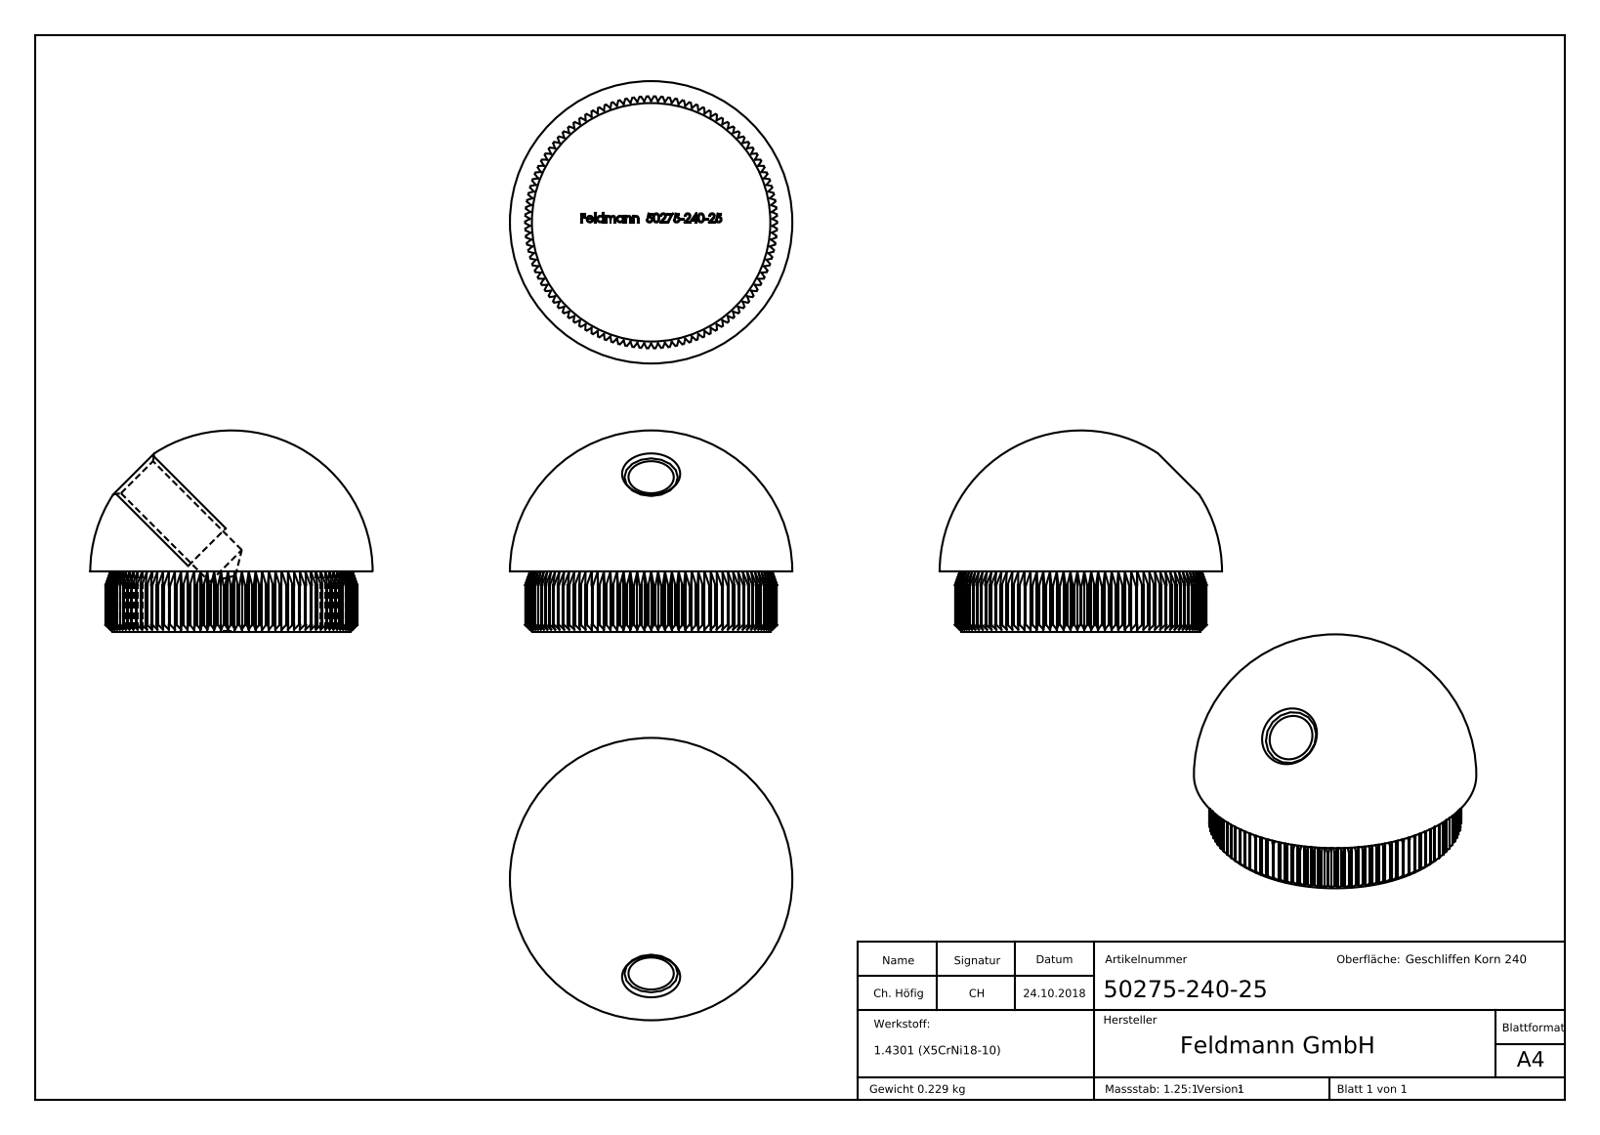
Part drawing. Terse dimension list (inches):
name: 50275-240-25
written by: SolidWorks 2015 (CONFIG_CONTROL_DESIGN)
unit: in
bodies: 1 solid, 592 faces (306 planar, 93 cylindrical, 193 other)
size: 1.669 × 1.669 × 1.189
volume: 1.769 in³; area: 9.711 in²
holes: 1× ⌀0.268
rounds: 1× R0.744
face distances: 0.717, 0.354, 0.717, 0.717, 0.716, 0.716, 0.35, 0.358, 0.052, 0.017
